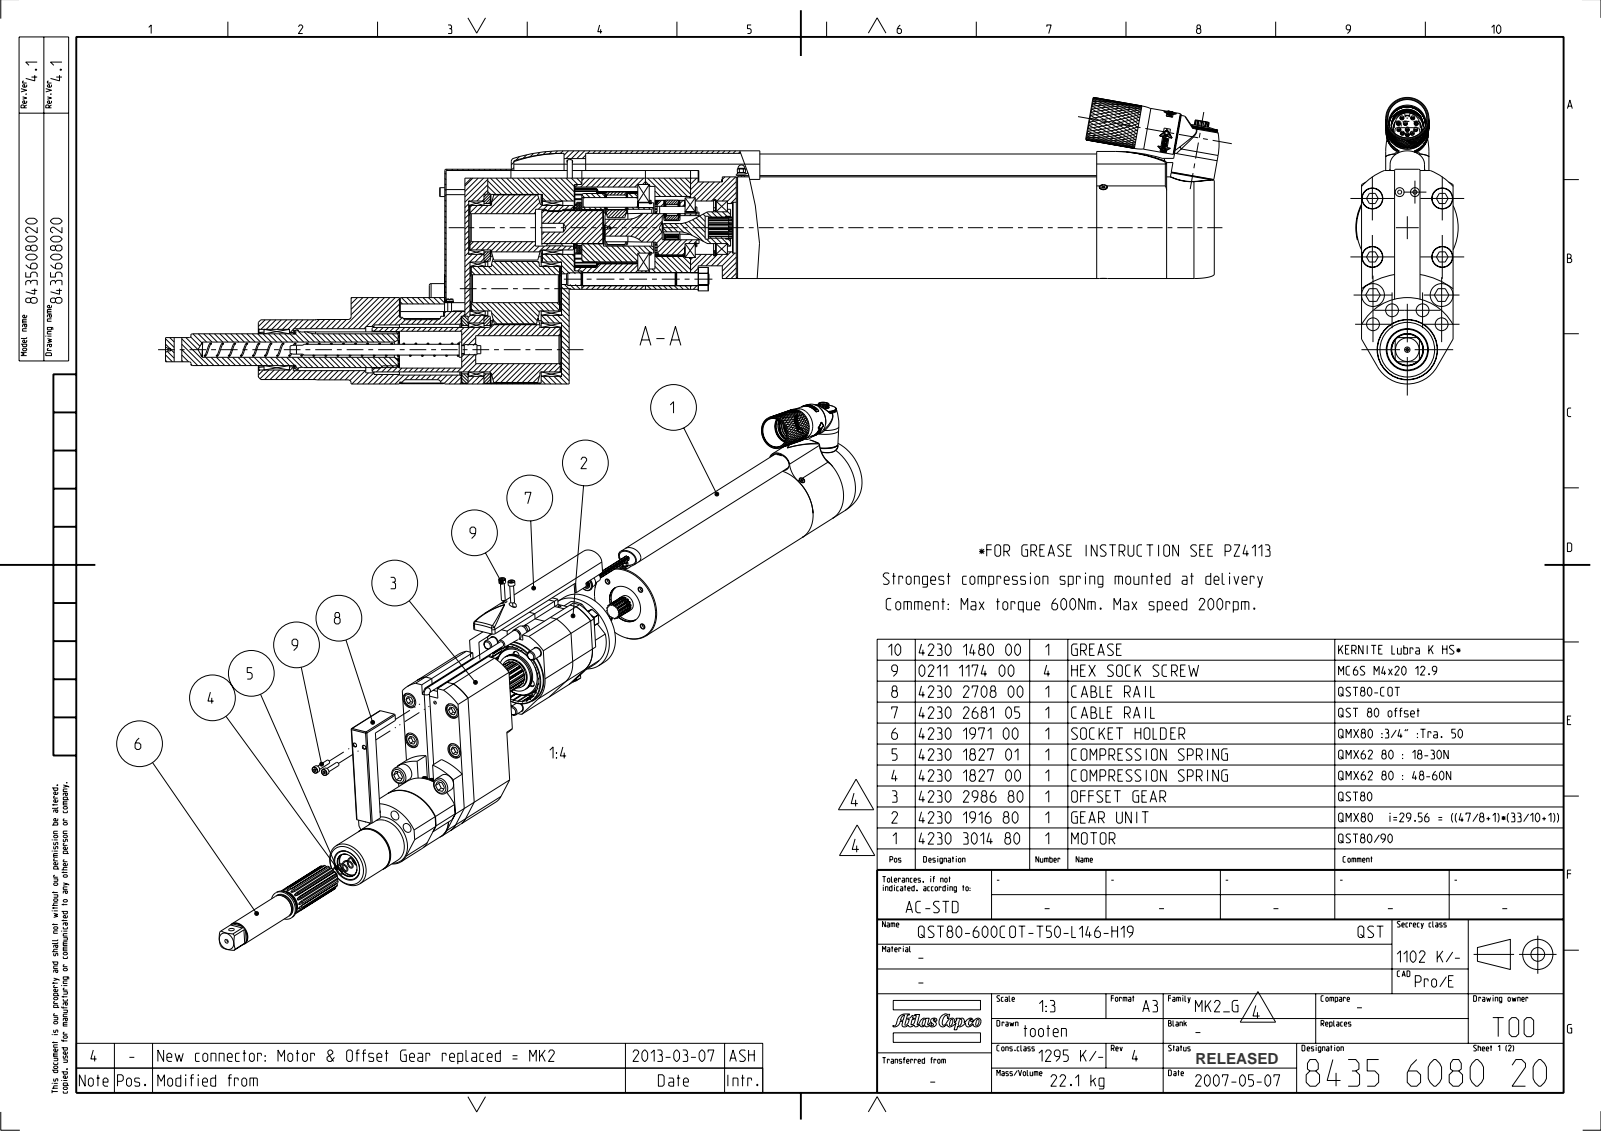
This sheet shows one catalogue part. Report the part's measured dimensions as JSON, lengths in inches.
{"part_name": "QST80_600_COT_BODY_50; QST80_REARCOVER_00; QST_CONNECTOR_02; QST80_SOCKETHOLDER_146_20 (+1 more)", "step_written_by": "PRO/ENGINEER BY PARAMETRIC TECHNOLOGY CORPORATION, 2012420 (CONFIG_CONTROL_DESIGN)", "units": "inches", "bodies": {"solids": 5, "faces": 3574, "planar": 1389, "cylindrical": 1103, "other": 1082}, "overall_size": [32.629, 8.879, 3.15], "volume_in3": 177.8, "surface_area_in2": 869.7, "round_holes": [[0.33, 9], [0.413, 9], [0.13, 7], [0.406, 7], [0.128, 6], [0.398, 6], [0.65, 5], [0.138, 4], [0.177, 4], [0.248, 4], [0.055, 3], [0.194, 3]], "round_bosses_or_shafts": [[0.394, 11], [0.63, 6], [0.236, 6], [0.098, 5], [0.276, 4], [0.157, 4], [0.118, 4], [0.472, 3]], "partial_cylinders_radius": [[0.008, 66], [0.011, 12], [0.02, 12], [0.039, 8], [0.031, 4], [0.047, 4], [0.059, 4], [0.207, 4]], "face_to_face_distances": [2.835, 0.039, 0.157, 1.024, 0.236, 3.228, 19.823, 17.165, 0.748, 2.657], "hole_center_spacings": [0.258, 1.18, 1.411, 1.669, 1.758, 1.919, 2.589, 0.472]}
